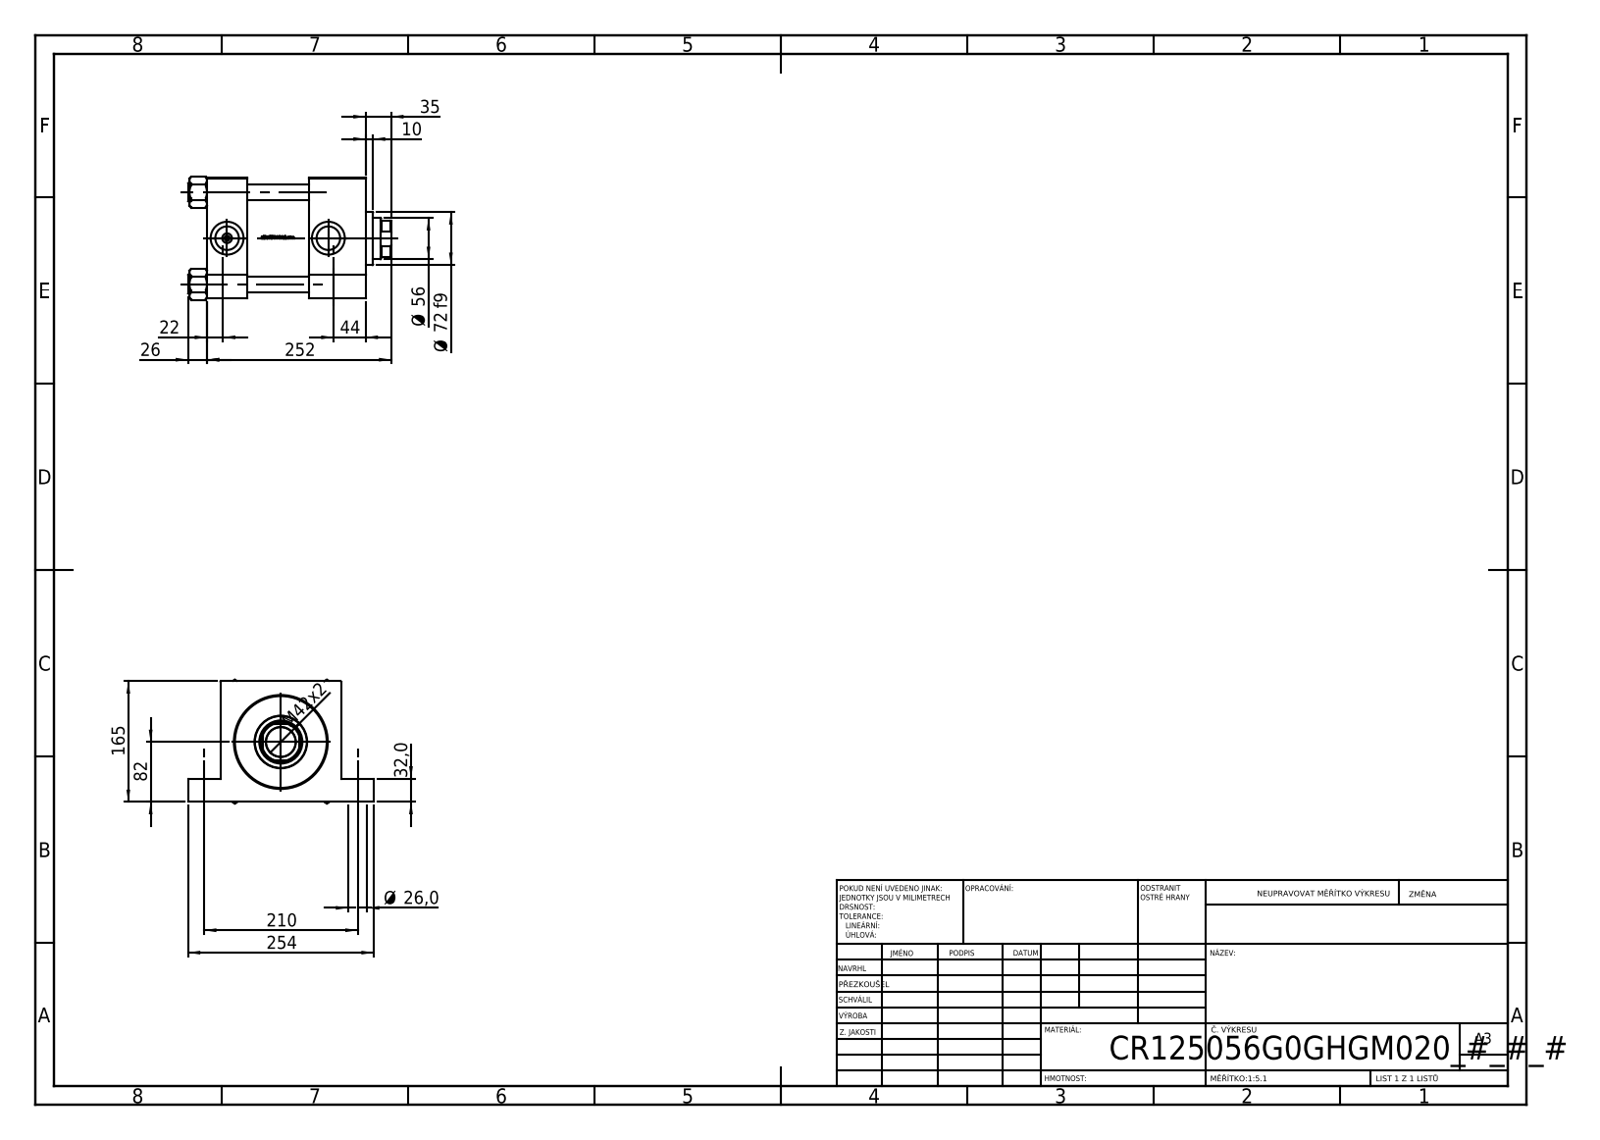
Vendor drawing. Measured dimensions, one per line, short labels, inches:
name: V215CR_G_Body; V215CR_G_TYCINKA; V215CR_VCP_G; V215_VC_A (+1 more)
written by: SolidWorks 2019 (CONFIG_CONTROL_DESIGN)
unit: in
bodies: 11 solids, 1135 faces (479 planar, 124 cylindrical, 532 other)
size: 10.945 × 10 × 6.659
volume: 296 in³; area: 832 in²
holes: 4× ⌀0.866, 2× ⌀0.276, 2× ⌀1.024, 2× ⌀1.024, 2× ⌀1.269, 2× ⌀1.772, 1× ⌀1.594, 1× ⌀2.205, 1× ⌀2.323, 1× ⌀3.78, 1× ⌀4.921, 1× ⌀4.941
bosses: 4× ⌀0.984, 1× ⌀5.157, 1× ⌀2.835
rounds: 1× R1.063
face distances: 6.496, 2.165, 8.543, 6.378, 5.472, 3.307, 3.071, 7.413, 5.248, 1.941
hole spacings: 4.957, 3.491, 3.519, 5.945, 7.01, 8.268, 10.183, 5.453
